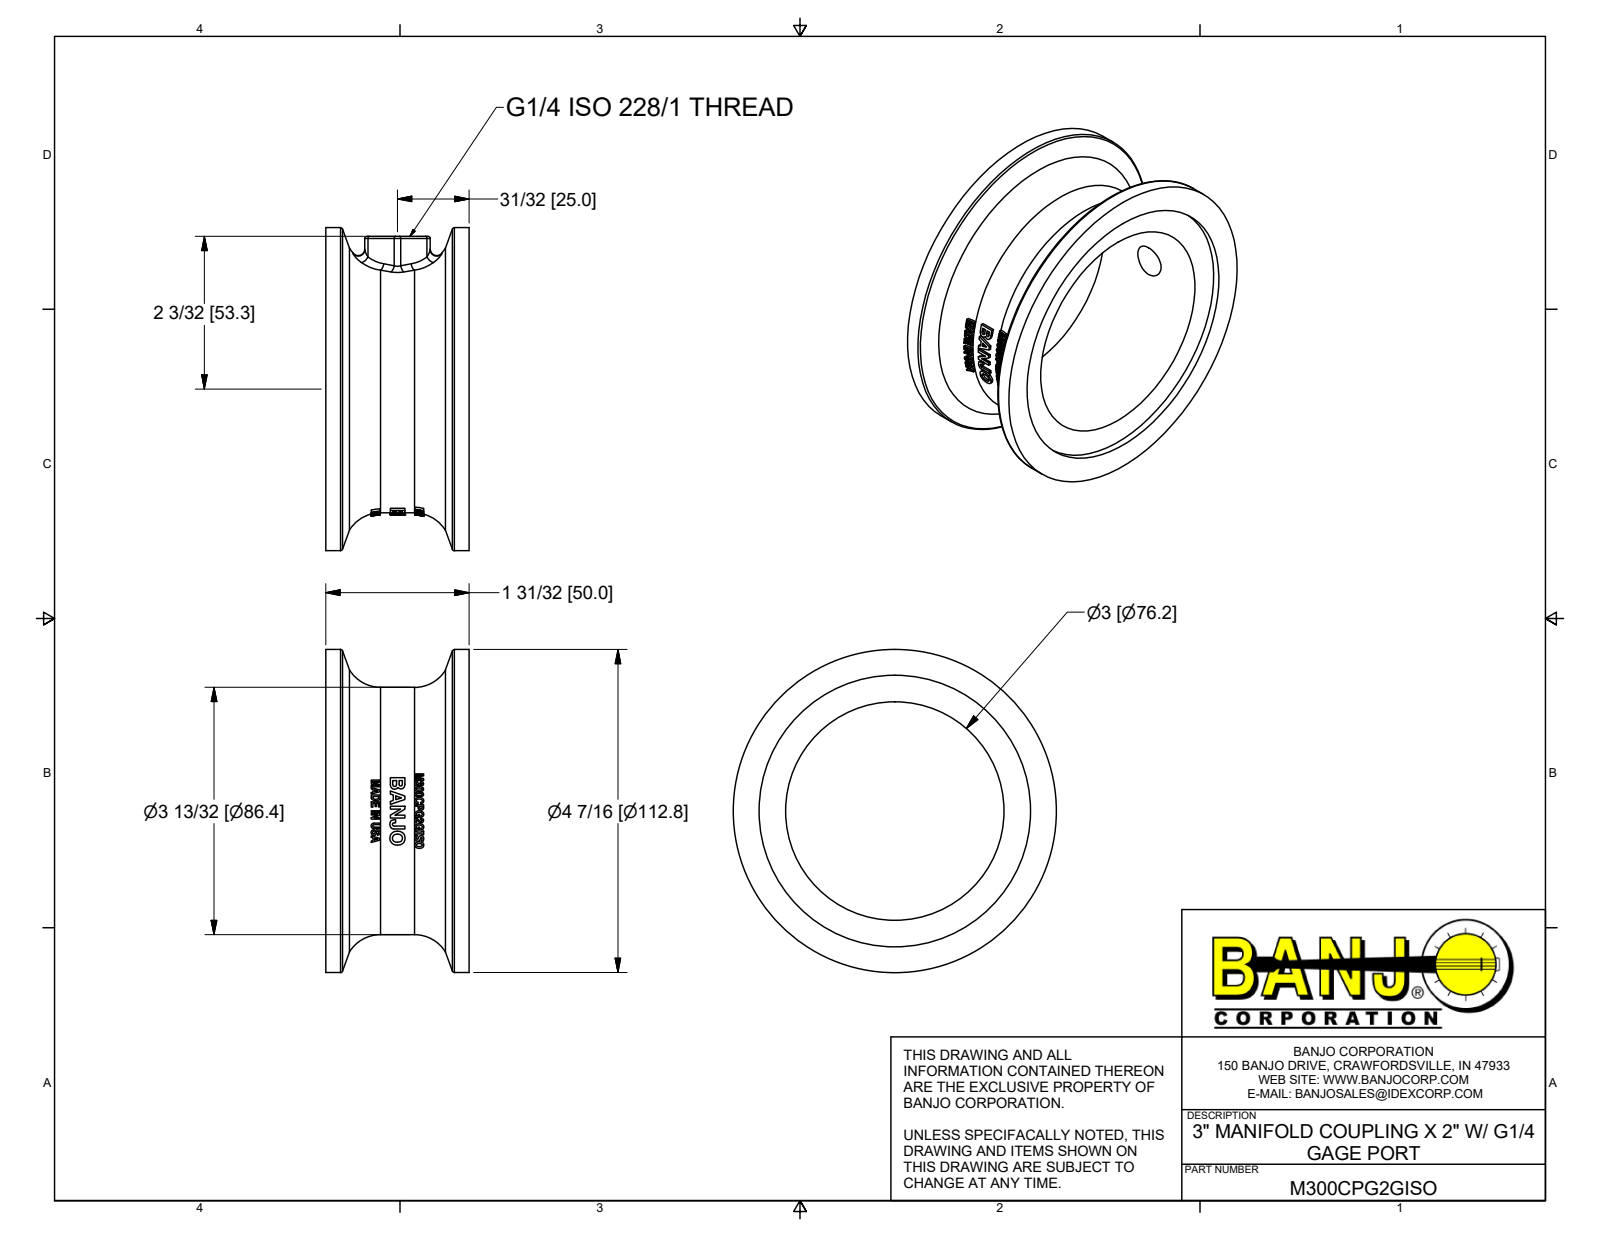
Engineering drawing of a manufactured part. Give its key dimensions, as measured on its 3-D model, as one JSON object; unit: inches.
{"part_name": "M300CPG2GISO; M300CPG2GISOX", "step_written_by": "Autodesk Inventor 2017 (AUTOMOTIVE_DESIGN)", "units": "inches", "bodies": {"solids": 1, "faces": 442, "planar": 185, "cylindrical": 28, "other": 229}, "overall_size": [4.44, 4.44, 1.969], "volume_in3": 7.823, "surface_area_in2": 68.15, "round_holes": [[0.451, 1], [3, 1], [3.73, 1]], "round_bosses_or_shafts": [[4.44, 1], [3.4, 1]], "partial_cylinders_radius": [[0.03, 6], [0.09, 6], [1.73, 1]], "face_to_face_distances": [0.1, 1.869, 1.969, 1.769, 0.9, 0.534, 0.434, 1.434, 1.334, 0.12]}
